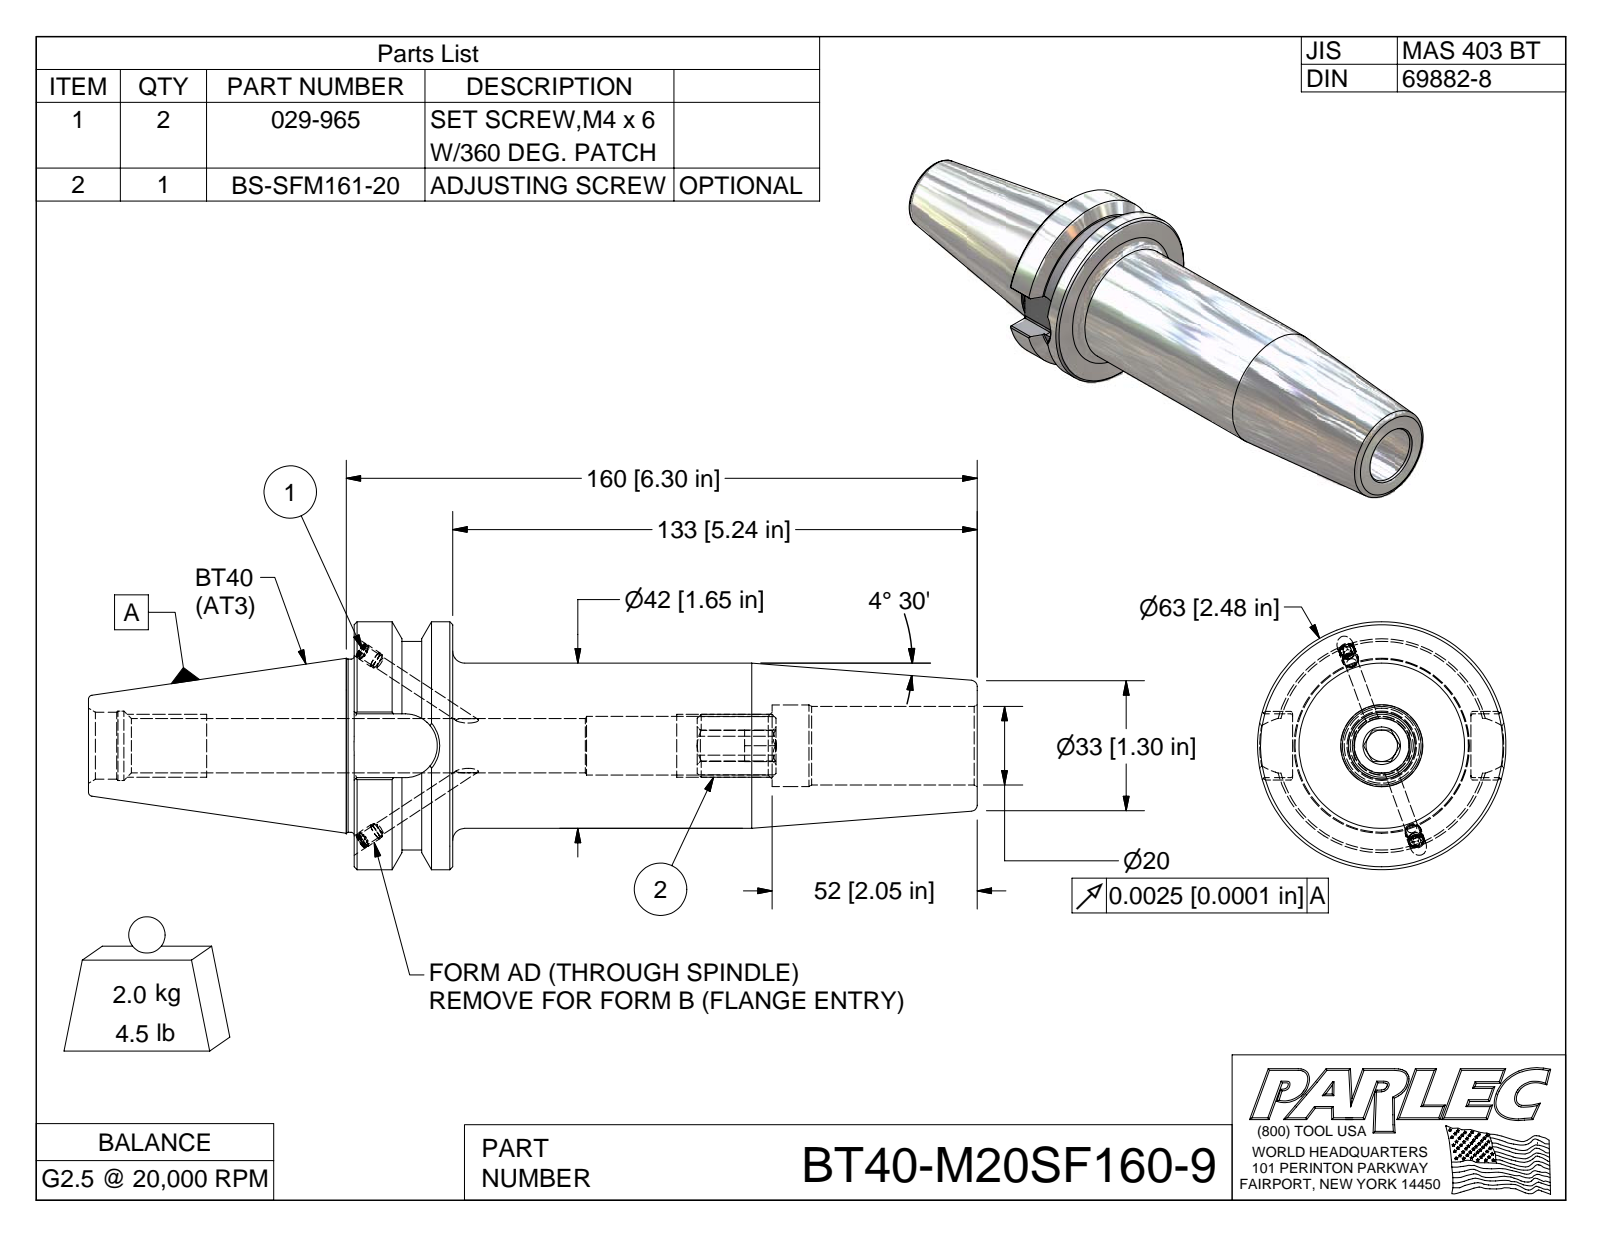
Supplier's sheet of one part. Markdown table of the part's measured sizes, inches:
| quantity | value |
| --- | --- |
| part name | BT40-M20SF160-9; BT40BC-M20SF160-9-1; 029-965; BS-SFM161-20 |
| STEP written by | Autodesk Inventor 2009 (AUTOMOTIVE_DESIGN) |
| units | inches |
| bodies | 4 solids, 131 faces (57 planar, 33 cylindrical, 41 other) |
| overall size | 8.874 × 2.48 × 2.48 |
| volume | 15.89 in³ |
| surface area | 74.2 in² |
| round holes (diameter × count) | 0.13 × 2, 0.161 × 2, 0.694 × 1, 0.786 × 1, 0.816 × 1 |
| round bosses / shafts (diameter × count) | 0.165 × 2, 0.157 × 2, 2.48 × 1, 2.087 × 1, 1.75 × 1, 1.73 × 1, 1.654 × 1 |
| partial cylindrical surfaces (radius × count) | 0.02 × 8, 0.315 × 1, 0.319 × 1 |
| main face-to-face distances | 0.984, 6.221, 5.237, 0.615, 1.166, 1.78, 2.653, 3.637, 8.874, 0.551 |
